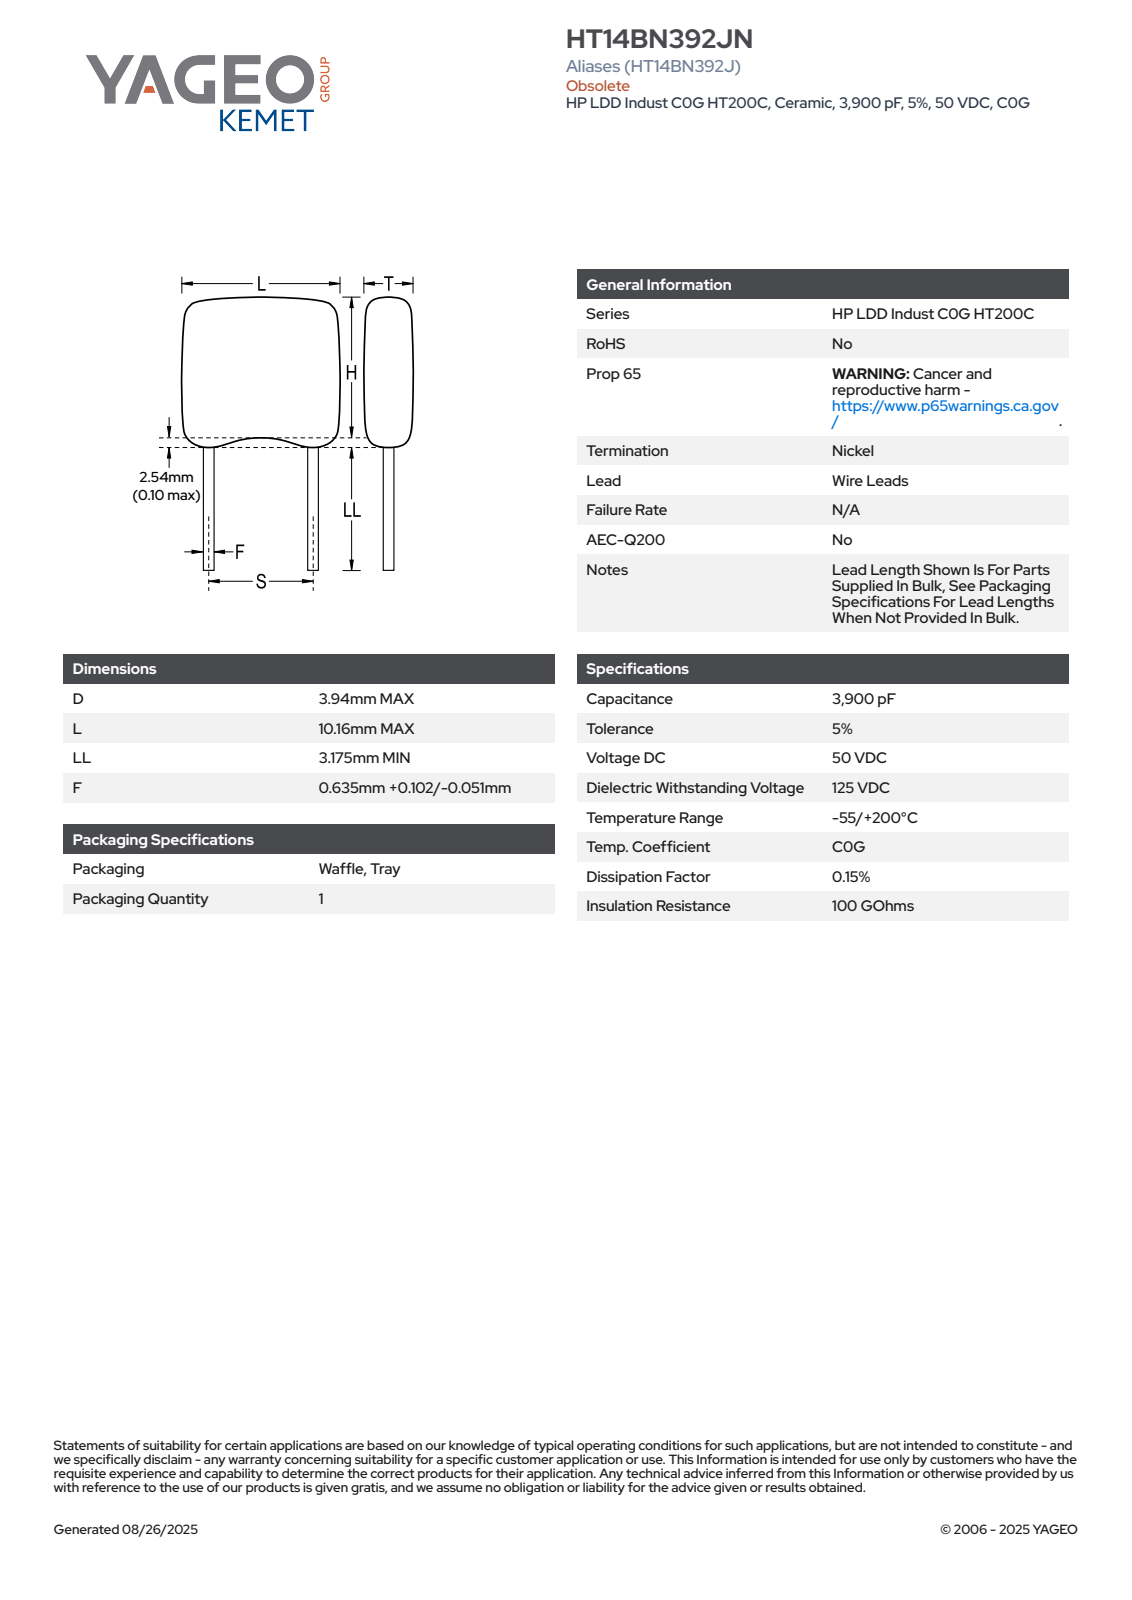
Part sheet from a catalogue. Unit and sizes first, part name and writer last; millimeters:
Units: millimetres
Overall size (bounding box): 73.66 × 3.95 × 3.94
Round bosses / shafts (diameter × count): ⌀3.94 ×1, ⌀0.64 ×1
Partial cylindrical surfaces — rounded edges, fillets, slot ends (radius × count): R1.98 ×1
Main face-to-face distances: 10.16, 31.75, 41.91, 73.66, 32.64, 0.89, 9.27, 41.02, 33.45, 1.7
Volume: 144 mm³ · Surface area: 277 mm²
Bodies: 1 solid, 67 faces (26 planar, 10 cylindrical, 31 other)
Part name (STEP PRODUCT): CCA_AMST_HT14_D3.94L10.16LL31.75F0.635
STEP written by: SolidWorks 2014 (AUTOMOTIVE_DESIGN)
